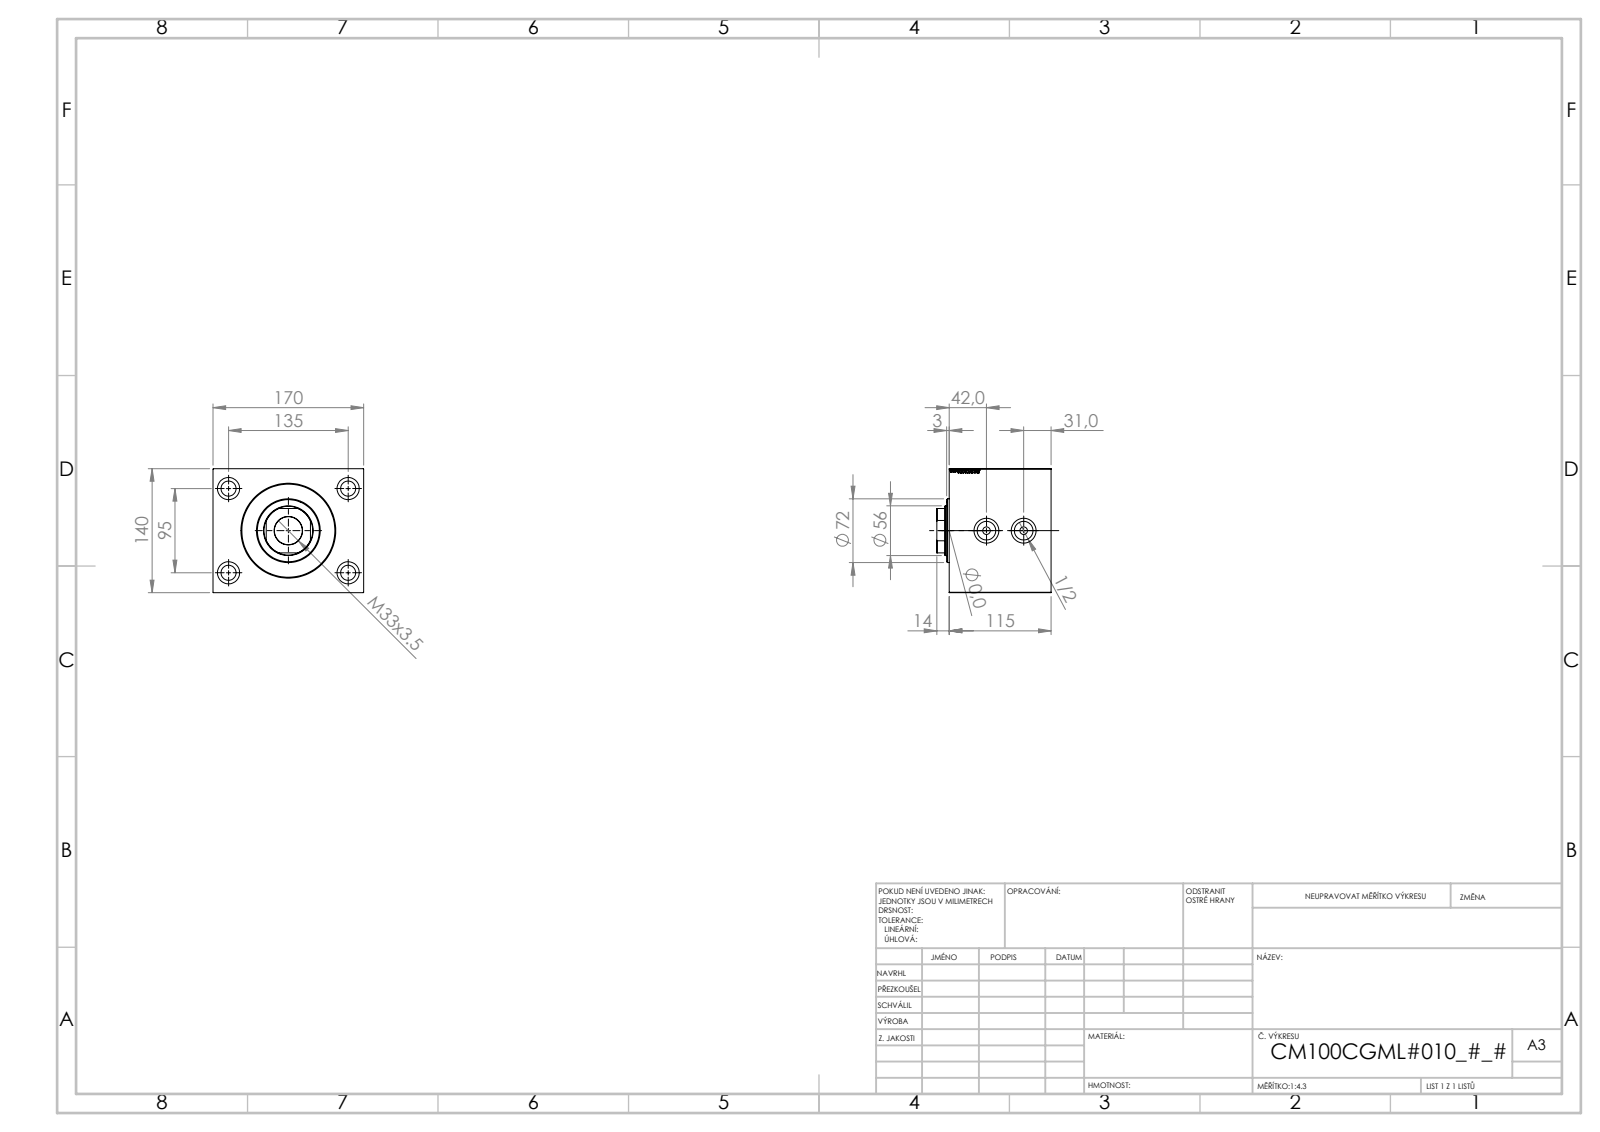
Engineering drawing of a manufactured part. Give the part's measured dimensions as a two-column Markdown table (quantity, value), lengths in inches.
| quantity | value |
| --- | --- |
| part name | V450CM_VC_B; V450CM_C_Body; V450CM_C_VCP |
| STEP written by | SolidWorks 2019 (CONFIG_CONTROL_DESIGN) |
| units | inches |
| bodies | 3 solids, 866 faces (410 planar, 62 cylindrical, 394 other) |
| overall size | 6.693 × 5.512 × 5.118 |
| volume | 153.5 in³ |
| surface area | 342.3 in² |
| round holes (diameter × count) | 0.669 × 4, 0.984 × 4, 0.335 × 2, 0.825 × 2, 1.102 × 2, 1.24 × 1, 1.772 × 1, 1.909 × 1, 3.937 × 1, 4.016 × 1, 4.134 × 1 |
| round bosses / shafts (diameter × count) | 2.835 × 1 |
| partial cylindrical surfaces (radius × count) | 0.866 × 1 |
| main face-to-face distances | 5.512, 4.528, 2.116, 2.411, 6.693, 0.394, 0.787, 4.134, 1.722, 1.329 |
| hole center spacings | 3.25, 3.74, 5.315, 6.499, 1.654 |
